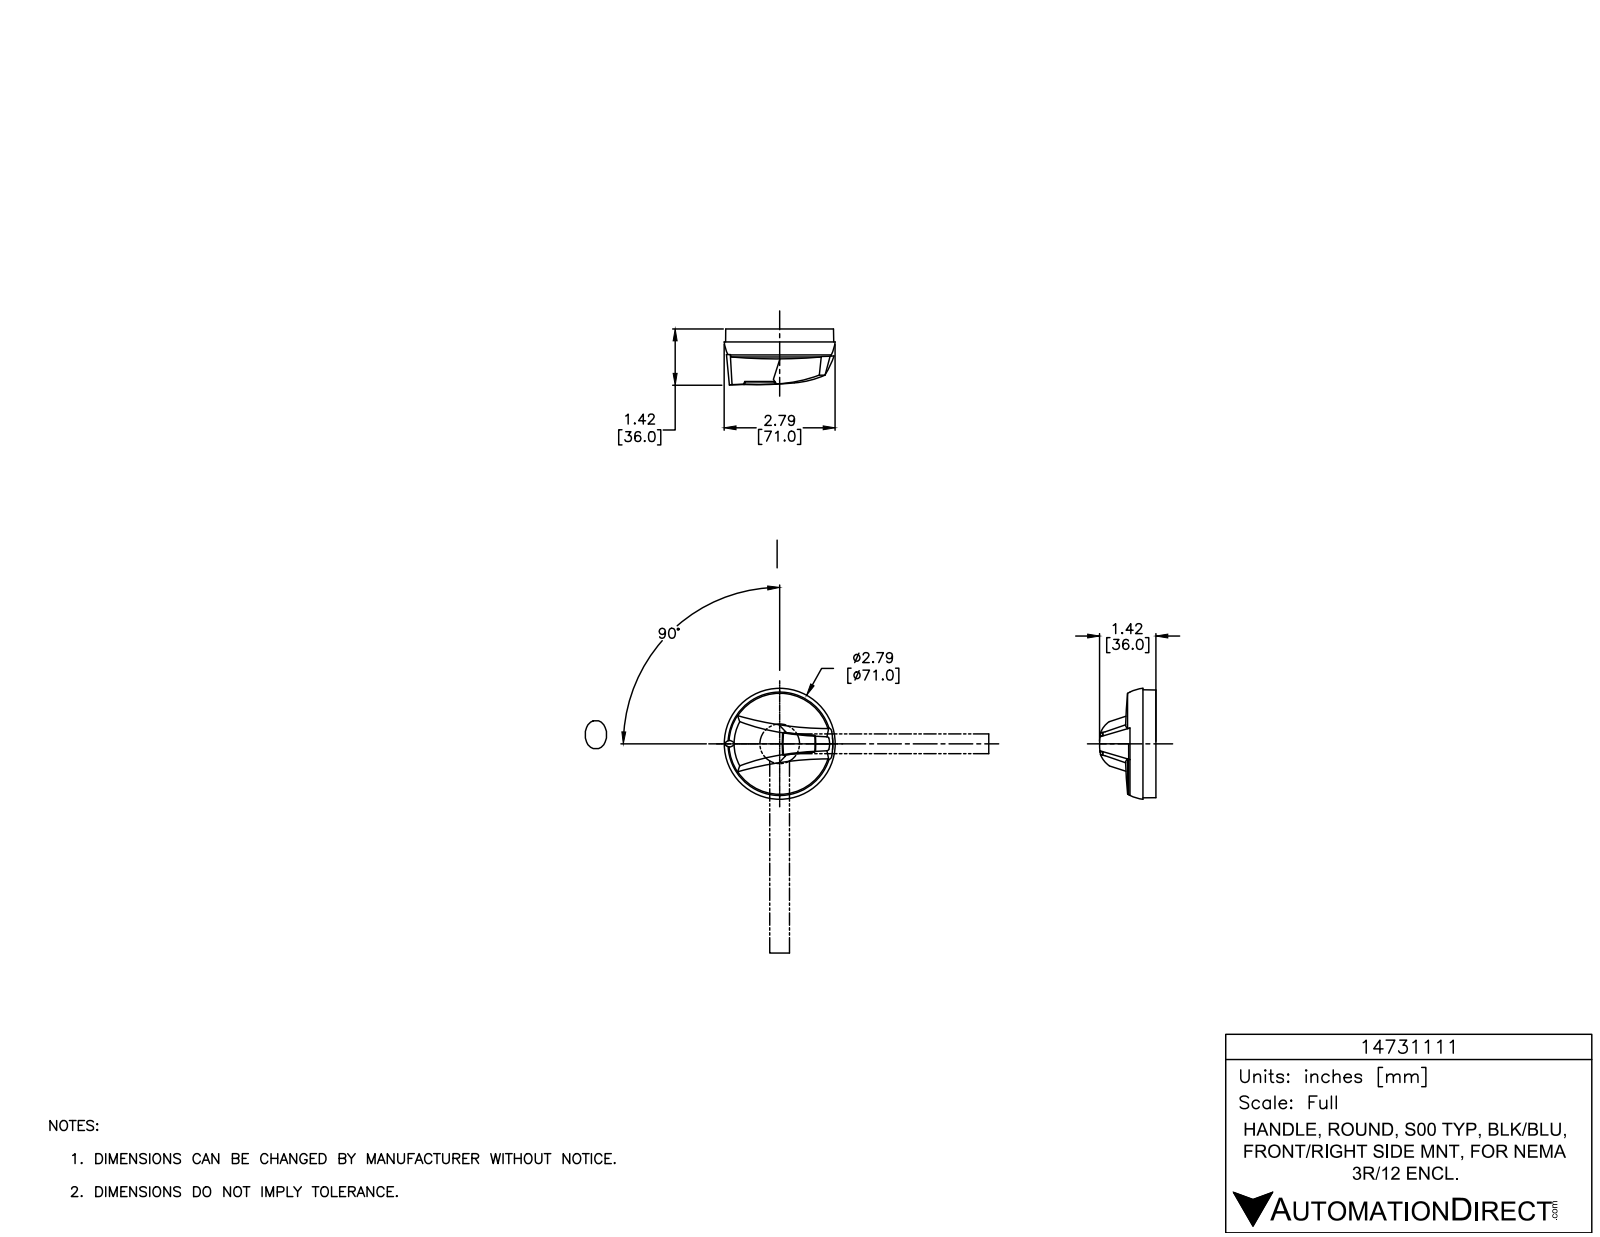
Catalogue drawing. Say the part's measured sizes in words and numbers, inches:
The part is named "14731111". Its 3-D file was written by "SolidWorks 2015 (AUTOMOTIVE_DESIGN)". It is 1 solid with 76 faces: 29 planar, 14 cylindrical and 33 other. Overall it measures 2.8 by 2.8 by 1.899 inches. Its volume is 5.42 cubic inches and its surface area 24.86 square inches. Round holes: 4 of diameter 0.169, 1 of diameter 0.457, 1 of diameter 2.618. Round bosses or shafts: 1 of diameter 0.801. The main face-to-face distances are 0.624, 0.616, 0.03, 0.646, 0.654, 0.488, 0.518, 1.134, 1.142, 0.807. The hole center spacings are 0.961, 1.102, 1.575, 1.922.
